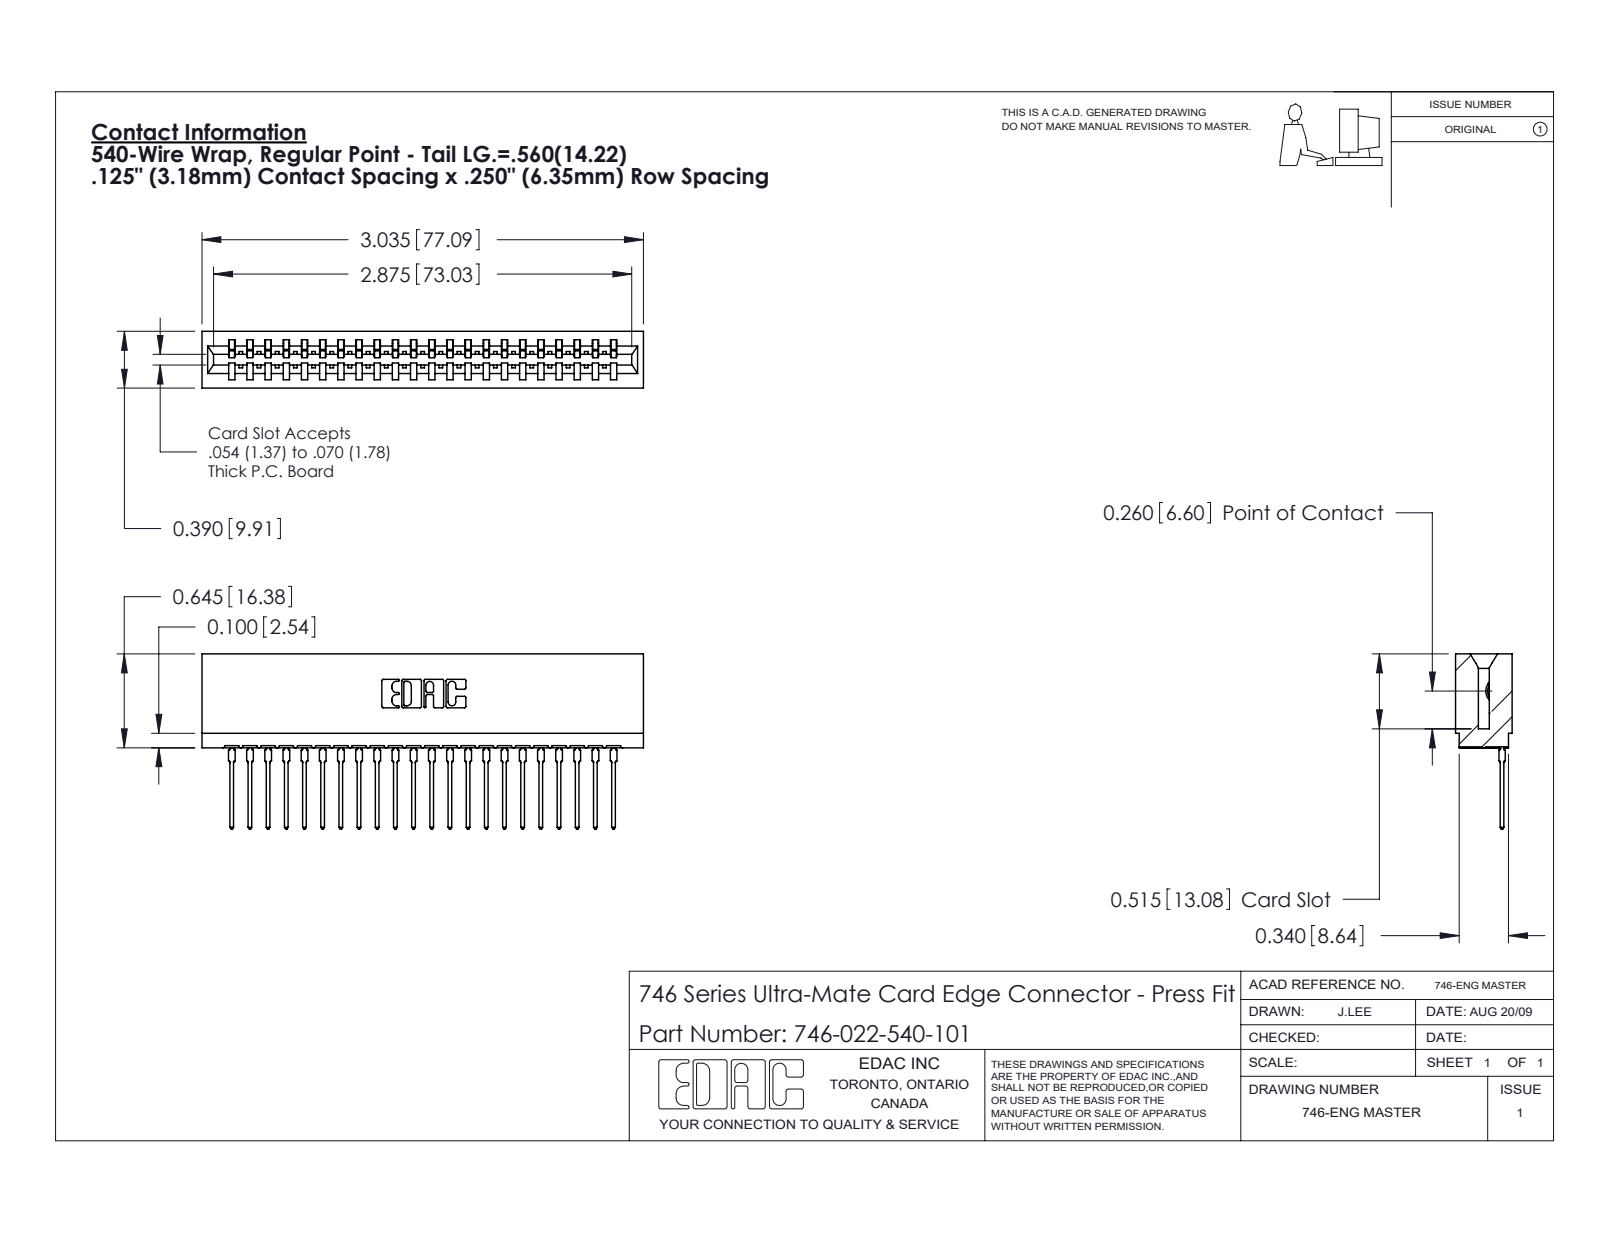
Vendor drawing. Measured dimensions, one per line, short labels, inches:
name: 746 Part_.515 Slot Depth - 01; 746-022-540-101; 746-292-001_540
written by: SolidWorks 2020 (CONFIG_CONTROL_DESIGN)
unit: in
bodies: 23 solids, 2473 faces (1441 planar, 460 cylindrical, 572 other)
size: 3.035 × 1.204 × 0.39
volume: 0.503 in³; area: 18.83 in²
rounds: 44× R0.021, 23× R0.015, 22× R0.01, 6× R0.007, 6× R0.031, 4× R0.005, 4× R0.011, 3× R0.026
face distances: 0.057, 0.333, 0.25, 0.39, 0.5, 0.025, 0.307, 0.125, 0.125, 0.083
